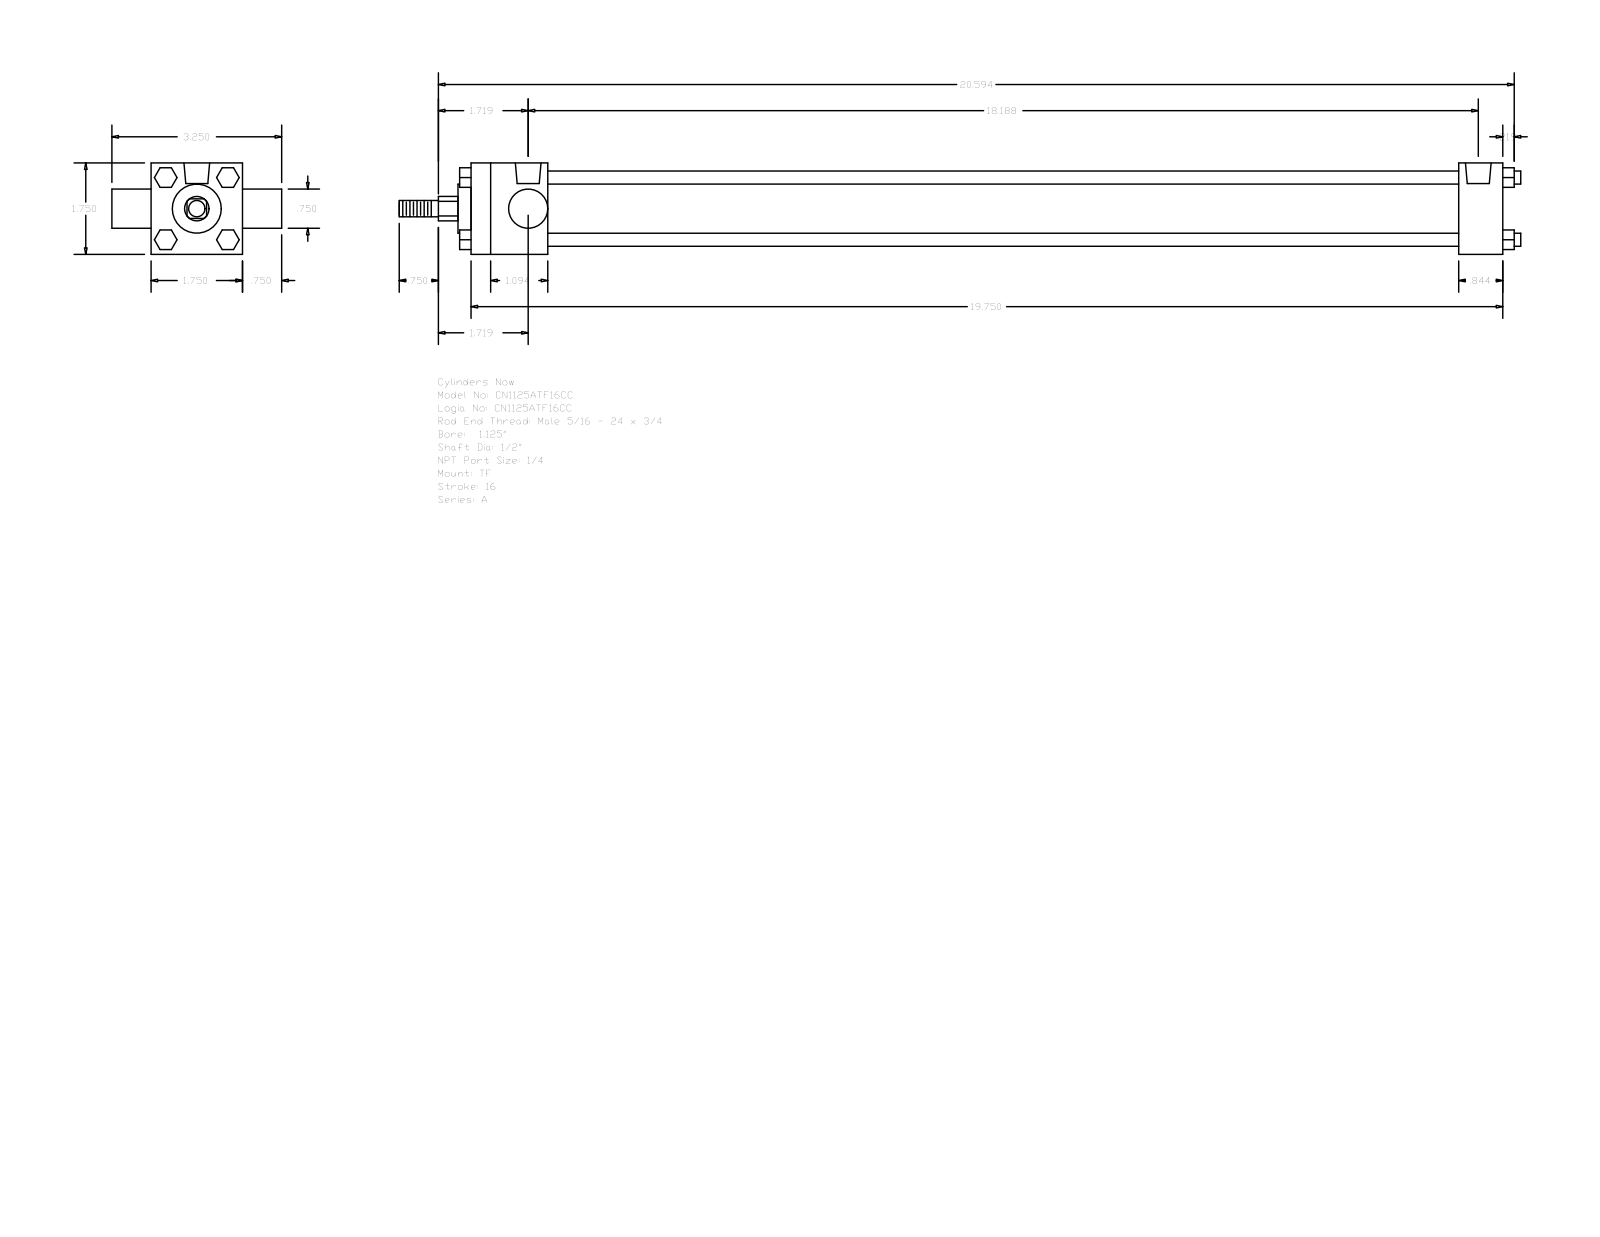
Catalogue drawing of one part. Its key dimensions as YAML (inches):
part_name: "A_TF__0112_0.5"
step_written_by: "GSSL Pune (CONFIG_CONTROL_DESIGN)"
units: inches
bodies: {solids: 0, faces: 120, planar: 92, cylindrical: 28, other: 0}
overall_size: [21.469, 3.25, 1.75]
round_holes:
  - {diameter: 0.219, count: 3}
  - {diameter: 0.492, count: 2}
round_bosses_or_shafts:
  - {diameter: 0.25, count: 4}
  - {diameter: 1.255, count: 1}
  - {diameter: 0.937, count: 1}
  - {diameter: 0.75, count: 1}
  - {diameter: 0.5, count: 1}
  - {diameter: 0.313, count: 1}
partial_cylinders:
  - {radius: 0.234, count: 1}
face_to_face_distances: [1.75, 19.75, 18.906, 0.844, 1.469, 17.437, 18.281, 0.75, 2.5, 0.375]
hole_center_spacings: [0.062, 0.063, 18.063, 18.125, 18.125, 18.187]
